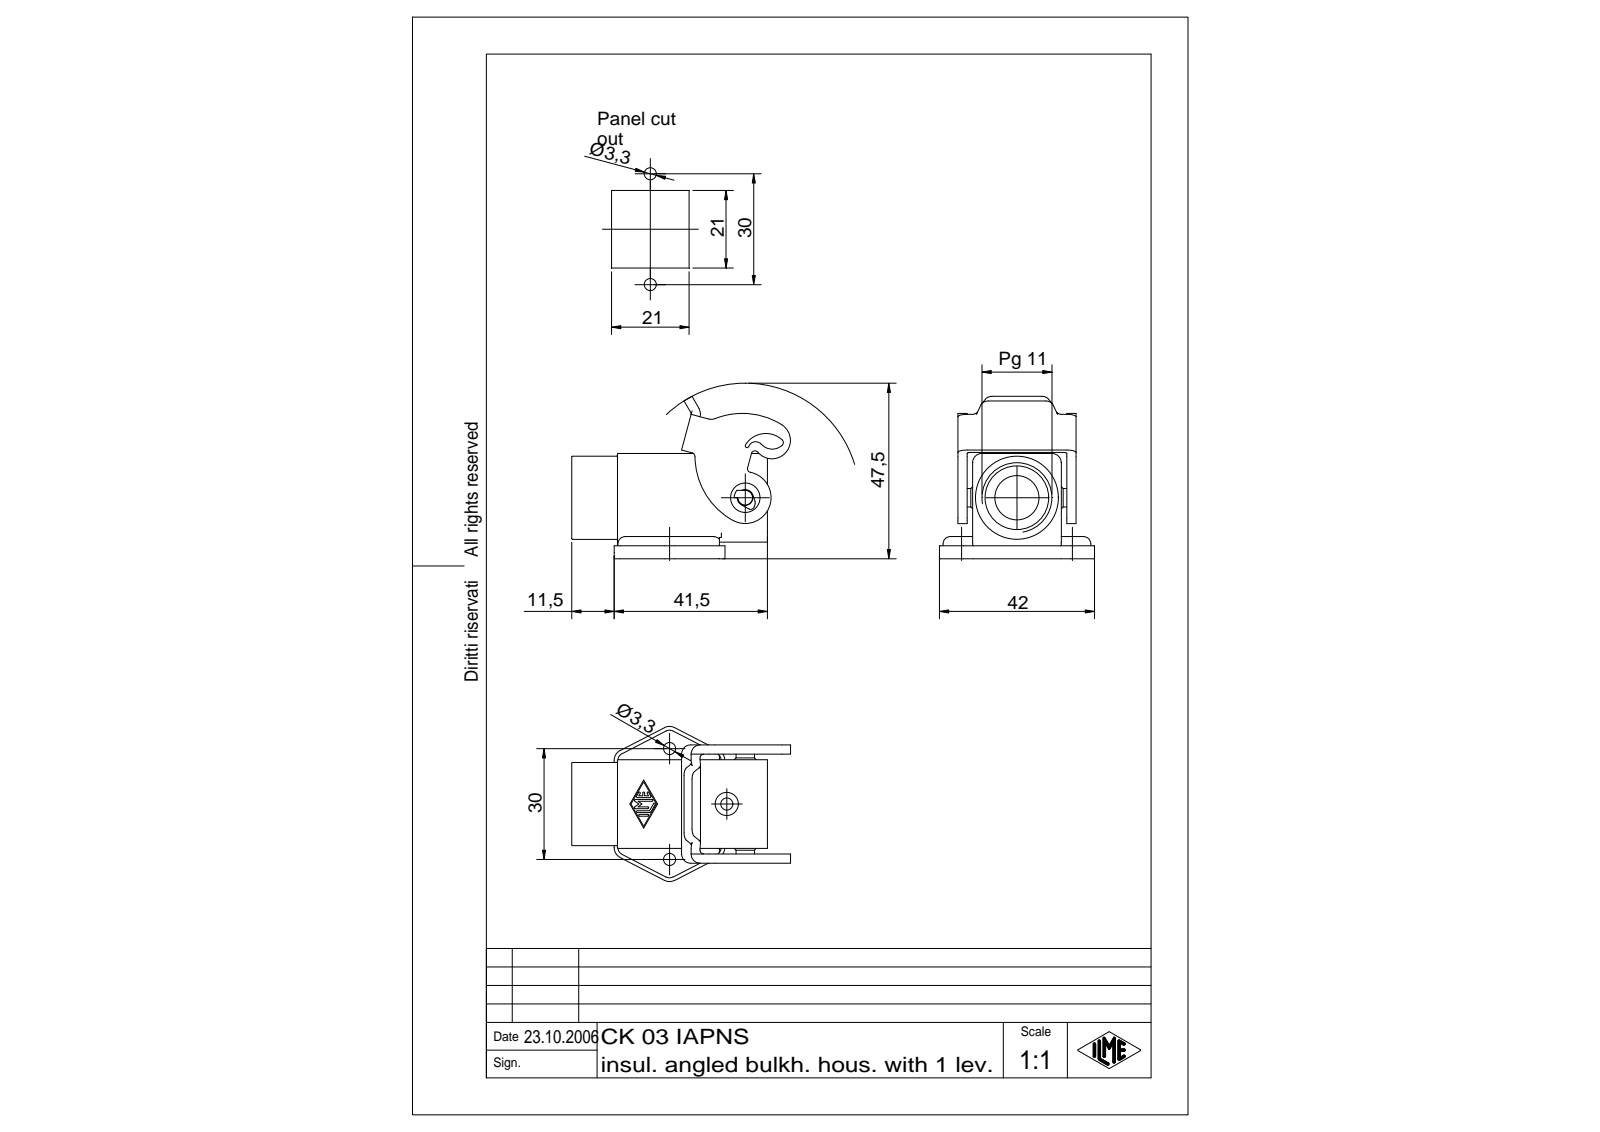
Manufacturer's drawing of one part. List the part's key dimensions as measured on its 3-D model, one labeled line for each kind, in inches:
Part name (STEP PRODUCT): CK 03 IAPNS
STEP written by: Autodesk Inventor 7 (AUTOMOTIVE_DESIGN)
Units: inches
Bodies: 1 solid, 339 faces (106 planar, 162 cylindrical, 71 other)
Overall size (bounding box): 2.333 × 1.73 × 1.654
Volume: 0.827 in³ · Surface area: 22.23 in²
Round holes (diameter × count): ⌀0.13 ×3, ⌀0.134 ×2, ⌀0.165 ×1, ⌀0.315 ×1, ⌀0.472 ×1, ⌀0.68 ×1
Round bosses / shafts (diameter × count): ⌀0.886 ×1, ⌀0.197 ×1, ⌀0.157 ×1
Partial cylindrical surfaces — rounded edges, fillets, slot ends (radius × count): R0.079 ×15, R0.01 ×14, R0.039 ×8, R0.069 ×8, R0.118 ×8, R0.008 ×7, R0.098 ×6, R0.049 ×5
Main face-to-face distances: 0.049, 0.896, 0.846, 0.945, 0.098, 0.059, 1.122, 1.102, 0.955, 0.108
Hole centre spacings: 0.849, 1.181
